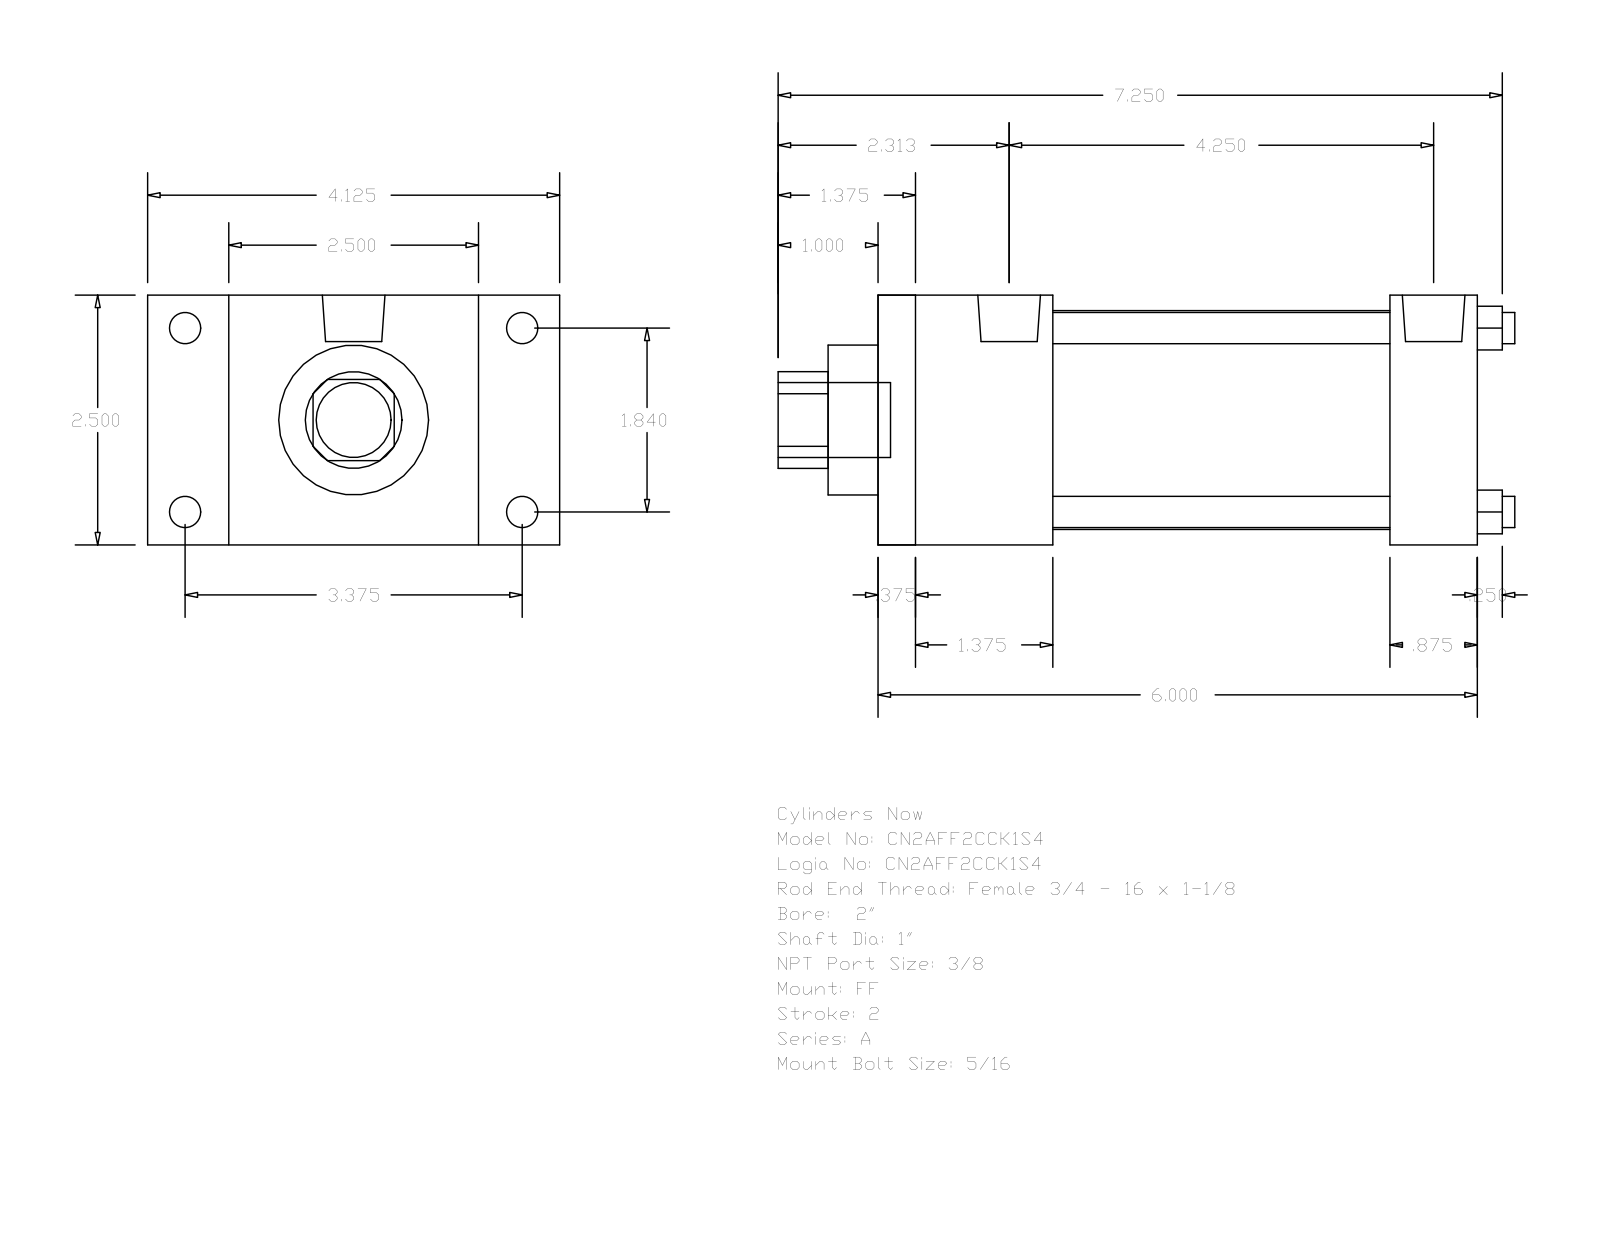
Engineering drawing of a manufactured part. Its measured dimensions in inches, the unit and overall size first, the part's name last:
Units: inches
Overall size (bounding box): 7.375 × 4.125 × 2.5
Round holes (diameter × count): ⌀0.313 ×4, ⌀1 ×1, ⌀1.5 ×1, ⌀2.19 ×1
Round bosses / shafts (diameter × count): ⌀0.313 ×4, ⌀0.219 ×4, ⌀0.627 ×2, ⌀0.75 ×1
Partial cylindrical surfaces — rounded edges, fillets, slot ends (radius × count): R0.484 ×1
Main face-to-face distances: 2.5, 6, 0.375, 5.625, 0.813, 1.75, 5.125, 1.375, 4.75, 3.375
Hole centre spacings: 1.301, 1.84, 2.602
Bodies: 0 solids, 92 faces (64 planar, 28 cylindrical, 0 other)
Part name (STEP PRODUCT): A_FF__0200_1
STEP written by: GSSL Pune (CONFIG_CONTROL_DESIGN)
